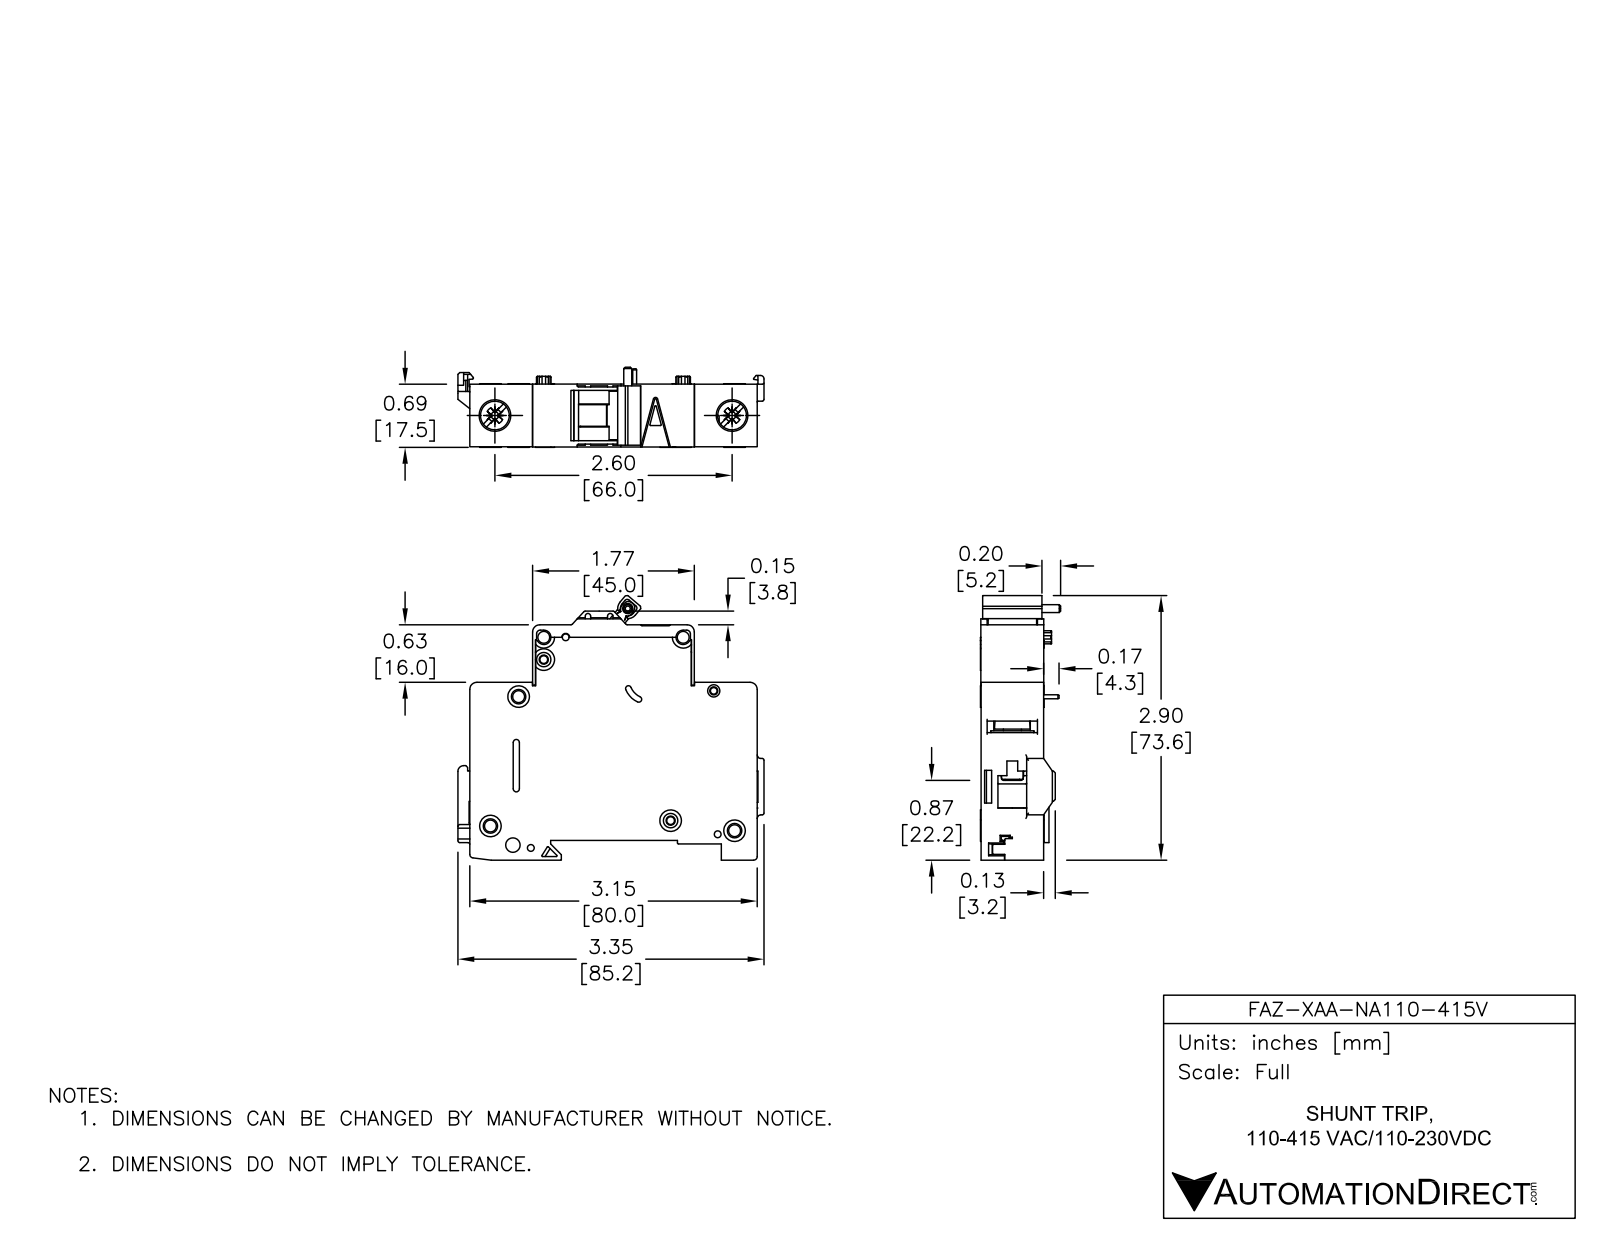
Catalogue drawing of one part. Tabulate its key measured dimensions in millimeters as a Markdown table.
| quantity | value |
| --- | --- |
| part name | FAZ-XAA-NA110-415 |
| STEP written by | SolidWorks 2014 (AUTOMOTIVE_DESIGN) |
| units | millimeters |
| bodies | 3 solids, 826 faces (406 planar, 288 cylindrical, 132 other) |
| overall size | 105 × 73.04 × 24.7 |
| volume | 77 757 mm³ |
| surface area | 24 729 mm² |
| round holes (diameter × count) | 3.6 × 5, 1.09 × 2, 1.5 × 2, 2.4 × 2, 4 × 2, 7.15 × 2, 8.2 × 2, 1.9 × 1, 2.15 × 1, 2.2 × 1, 2.55 × 1, 3.3 × 1 |
| round bosses / shafts (diameter × count) | 6 × 6, 3.6 × 2, 2.5 × 1, 1.1 × 1 |
| partial cylindrical surfaces (radius × count) | 0.5 × 30, 0.25 × 29, 1 × 12, 2 × 10, 5 × 5, 4 × 4, 1.8 × 3, 0.2 × 2 |
| main face-to-face distances | 17.5, 15.05, 0.7, 2.45, 1.75, 15.75, 13.3, 14, 12.6, 2 |
| hole center spacings | 6.2, 5.19, 6.1, 8.19, 8.56, 8.7, 11.11, 12.45 |
